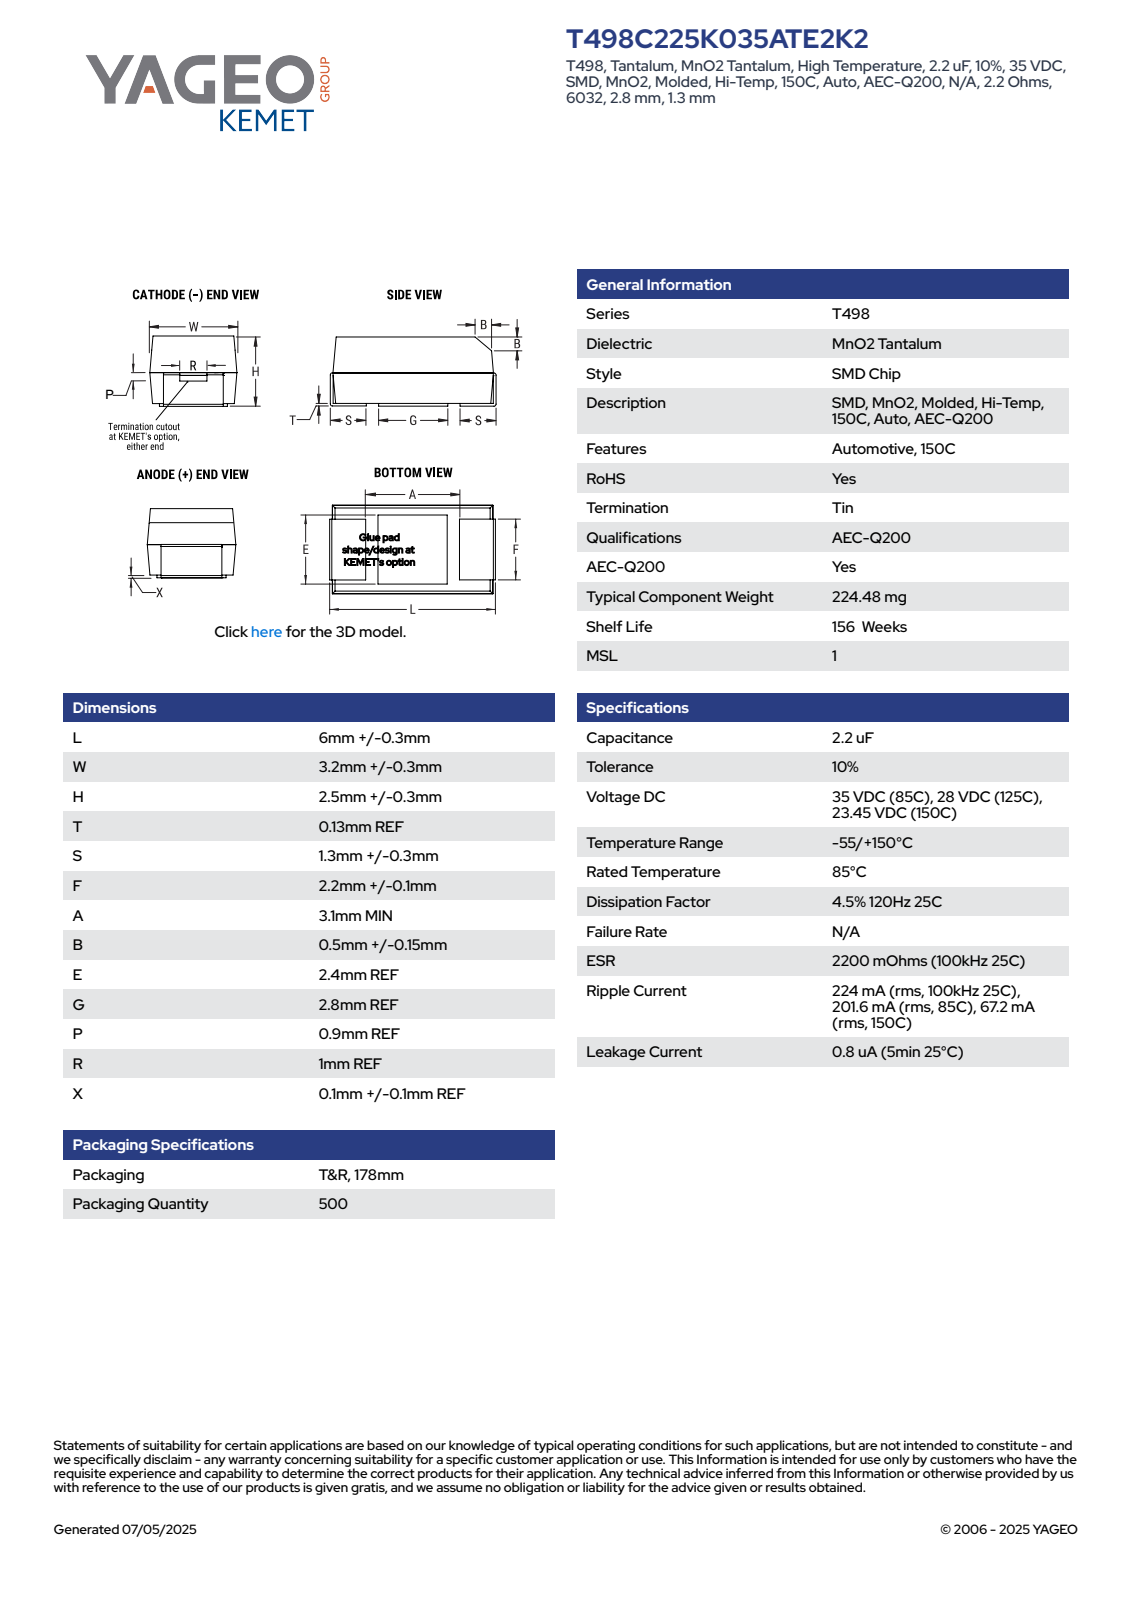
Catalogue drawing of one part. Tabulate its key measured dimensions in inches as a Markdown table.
| quantity | value |
| --- | --- |
| part name | CTSM_TCM2NK_6032_L6.3W3.5H2.8T0.13S1.3F2.3A3.1B0.65E2.4G2.8P0.9R1X0.2 |
| STEP written by | SolidWorks 2020 (AUTOMOTIVE_DESIGN) |
| units | inches |
| bodies | 4 solids, 100 faces (95 planar, 5 cylindrical, 0 other) |
| overall size | 0.248 × 0.138 × 0.111 |
| volume | 0.003 in³ |
| surface area | 0.167 in² |
| partial cylindrical surfaces (radius × count) | 0.004 × 4 |
| main face-to-face distances | 0.11, 0.102, 0.136, 0.137, 0.105, 0.243, 0.248, 0.238, 0.069, 0.179 |
